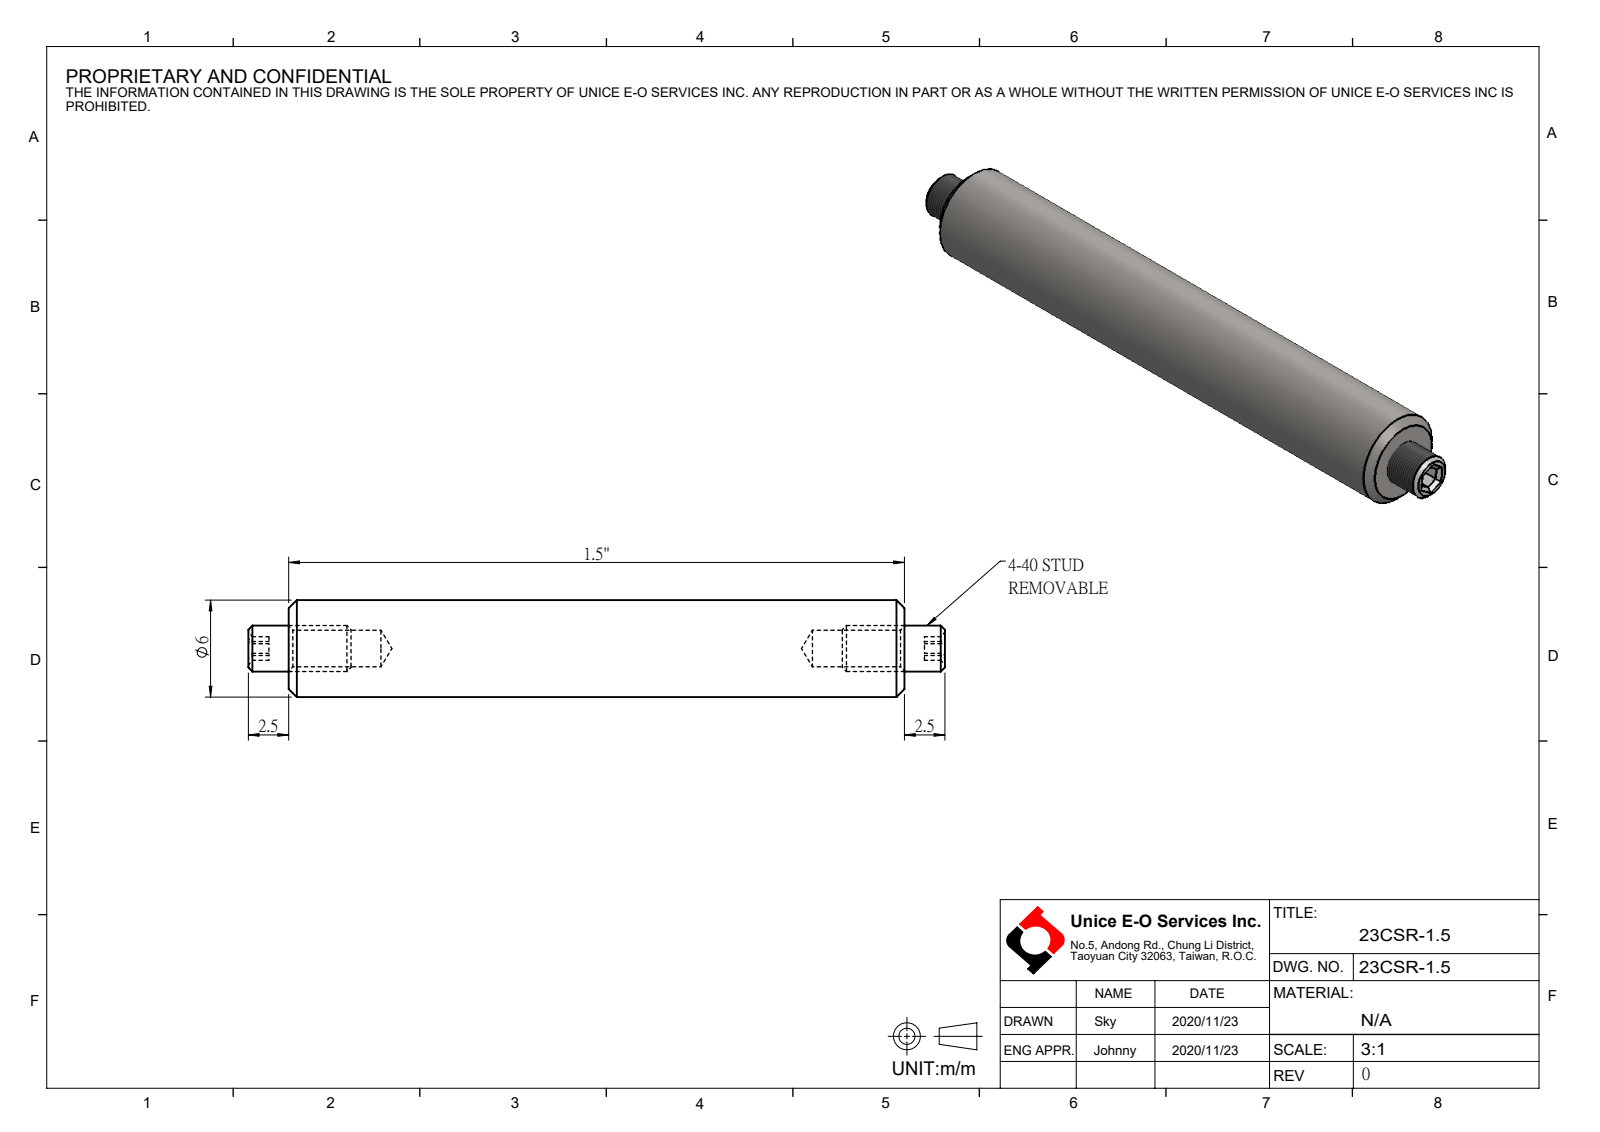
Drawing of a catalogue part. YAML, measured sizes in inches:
part_name: "23CSR-1.5"
step_written_by: "SolidWorks 2016 (AUTOMOTIVE_DESIGN)"
units: inches
bodies: {solids: 0, faces: 42, planar: 28, cylindrical: 6, other: 8}
overall_size: [1.697, 0.236, 0.236]
round_bosses_or_shafts:
  - {diameter: 0.236, count: 1}
  - {diameter: 0.112, count: 1}
face_to_face_distances: [1.5, 0.05, 0.098, 1.598, 1.697]
